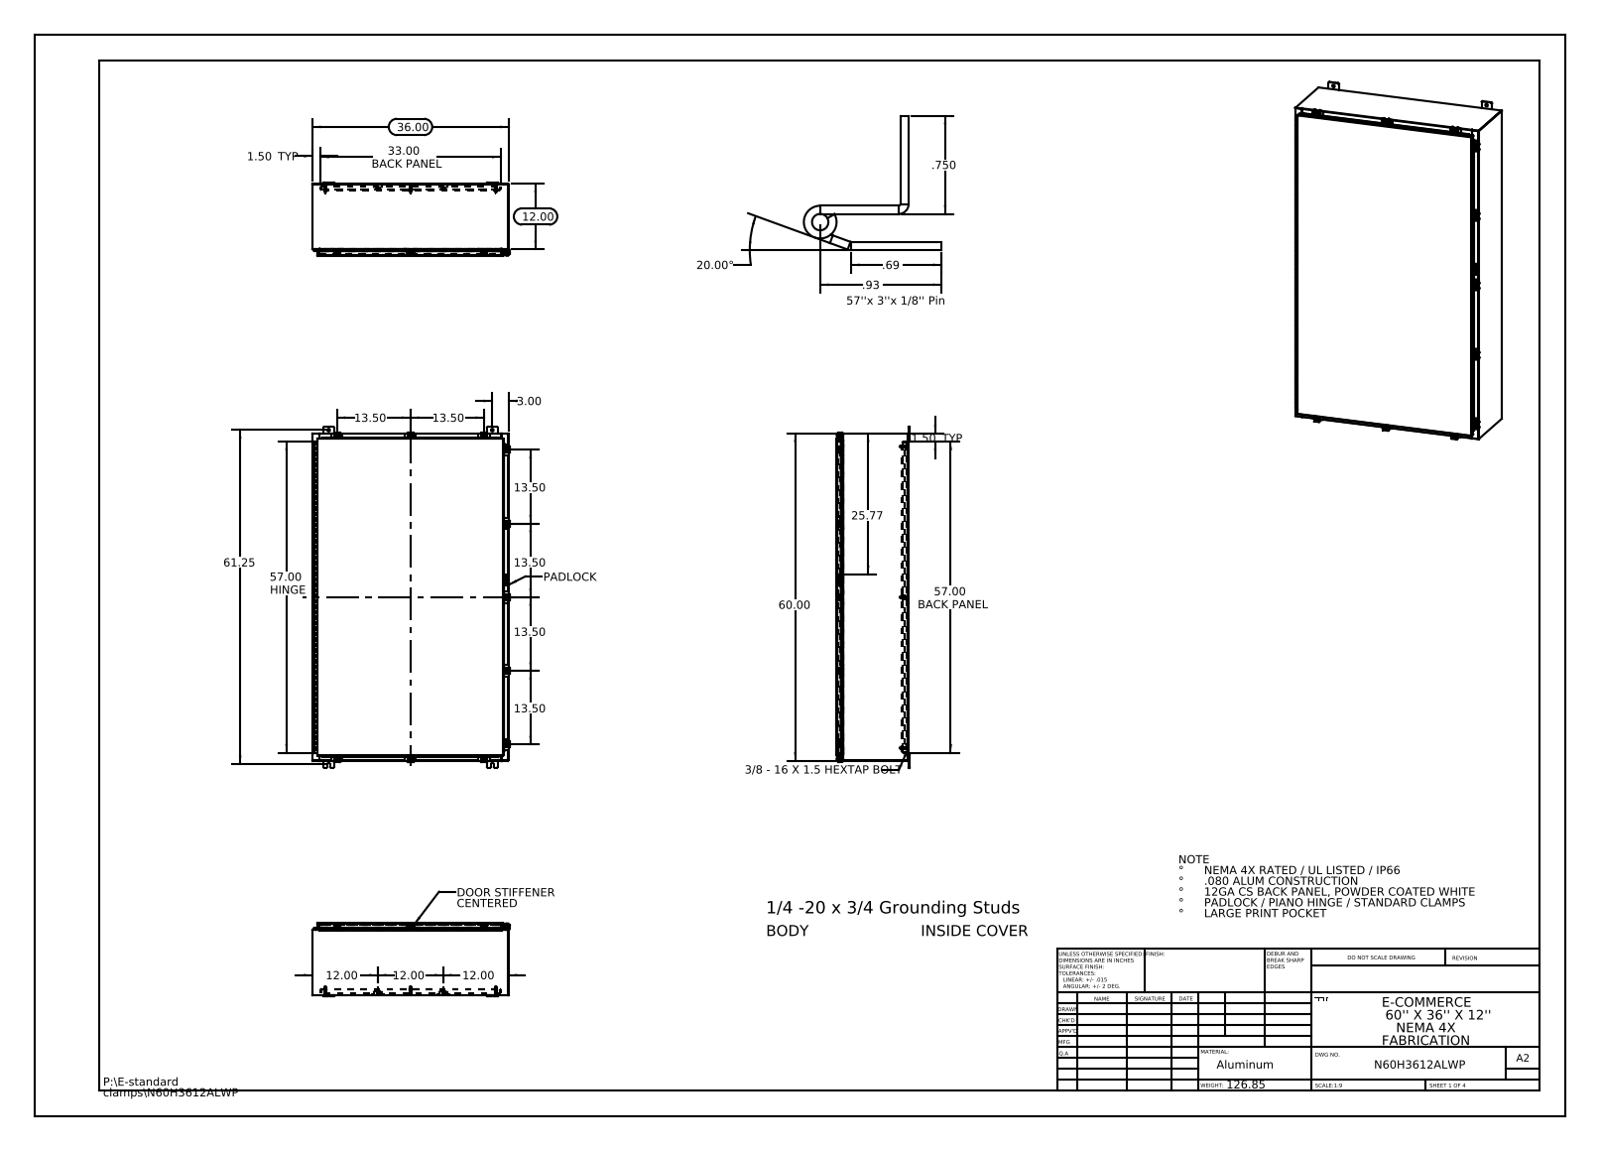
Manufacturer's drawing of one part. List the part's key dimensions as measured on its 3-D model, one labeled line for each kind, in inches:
Part name (STEP PRODUCT): N60H3612ALWP Padlock Hasp; N60H3612ALWP Clamp Bracket; N60H3612ALWP Mounting Feet; N60H3612ALWP 22104005_DEFAULT (+8 more)
STEP written by: SolidWorks 2013 (CONFIG_CONTROL_DESIGN)
Units: inches
Bodies: 79 solids, 3408 faces (1766 planar, 1466 cylindrical, 176 other)
Overall size (bounding box): 62.5 × 36.211 × 13.389
Volume: 796 in³ · Surface area: 19 851 in²
Round holes (diameter × count): ⌀0.5 ×12, ⌀0.213 ×11, ⌀0.26 ×11, ⌀0.25 ×8, ⌀0.125 ×2, ⌀0.125 ×1
Round bosses / shafts (diameter × count): ⌀0.25 ×12, ⌀0.5 ×11, ⌀0.399 ×11, ⌀0.625 ×8, ⌀0.375 ×8, ⌀0.33 ×8
Partial cylindrical surfaces — rounded edges, fillets, slot ends (radius × count): R0.06 ×50, R0.013 ×39, R0.088 ×33, R0.19 ×24, R0.12 ×22, R0.141 ×22, R0.05 ×17, R0.08 ×16
Main face-to-face distances: 0.075, 13.126, 13.051, 0.104, 13.201, 1, 12.126, 1.075, 12.051, 1.179
Hole centre spacings: 13.5, 13.663, 2.225, 27, 27.625, 29.802, 41.709, 57.39
